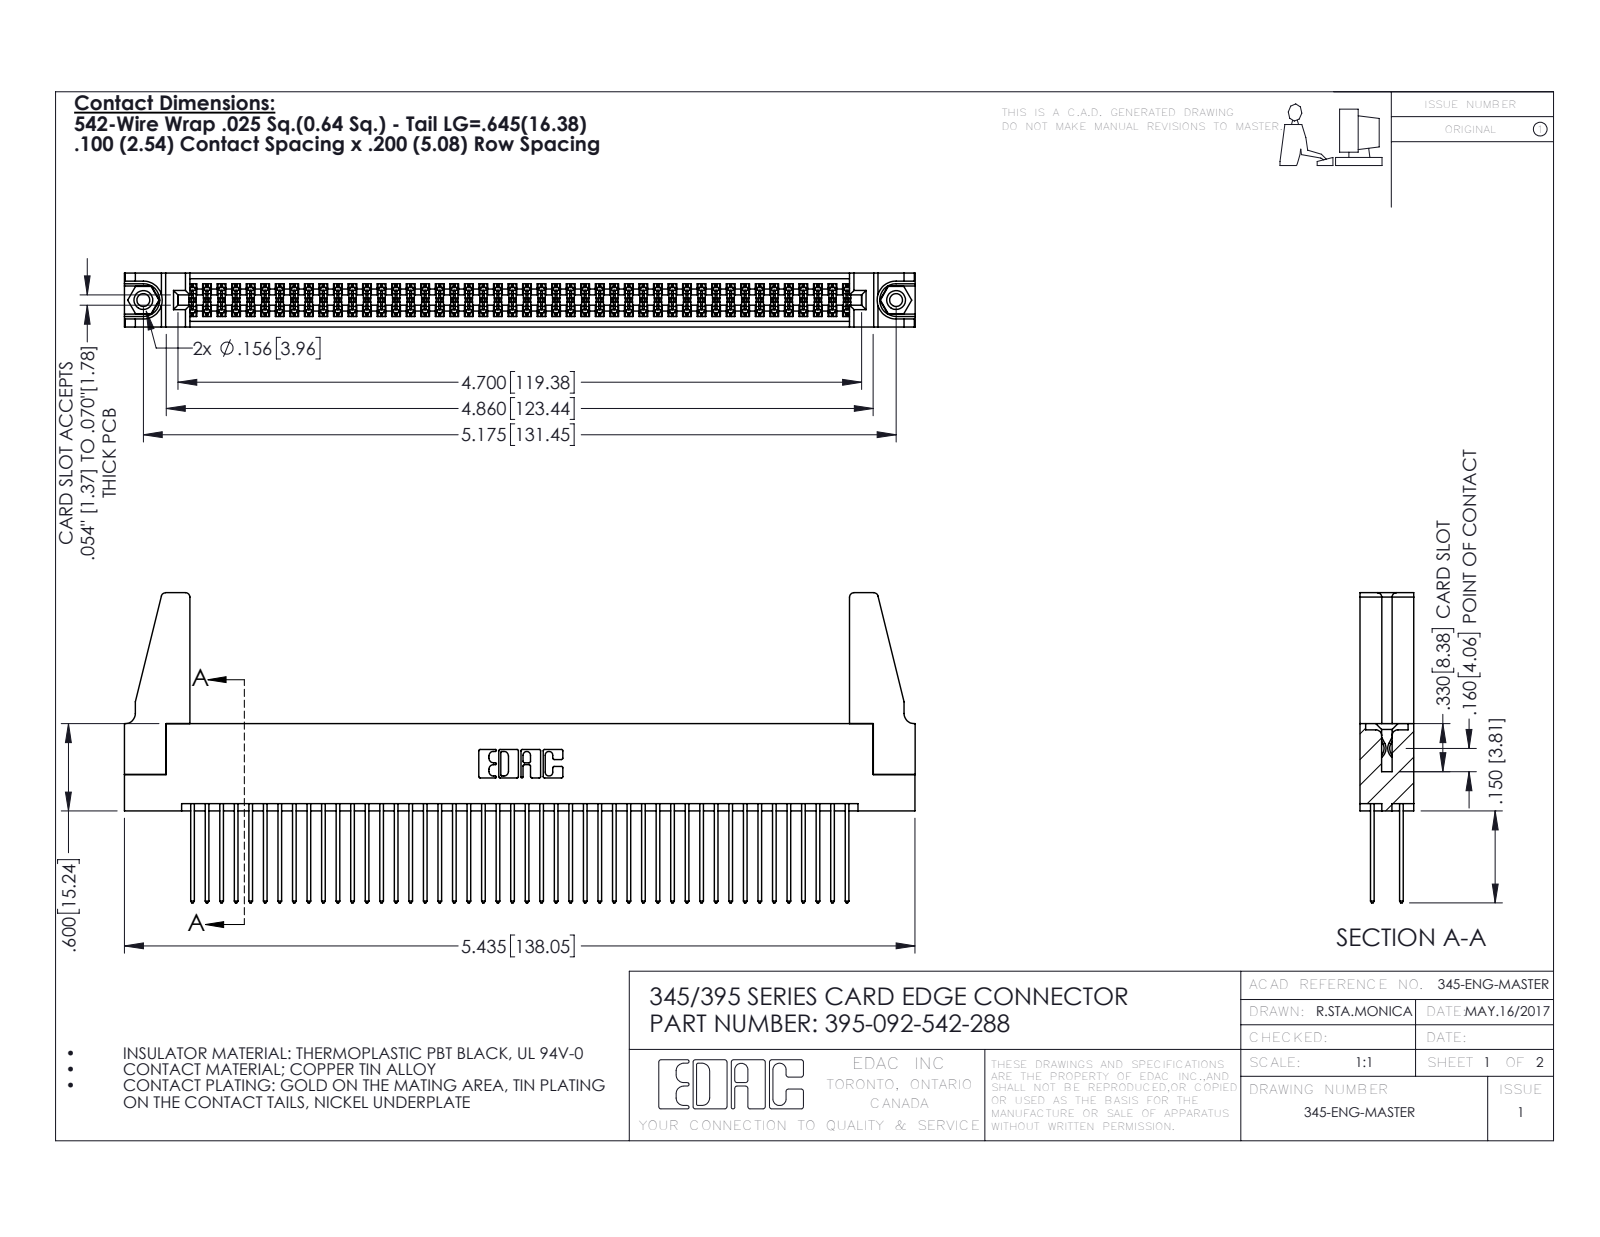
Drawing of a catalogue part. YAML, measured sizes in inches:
part_name: "395-092-542-288; 345-220-078_345-220-088; 345-292-001_345-293-142; 345 Part_Flush Mounting Lugs - 0.156 Dia-TH (+1 more)"
step_written_by: "SolidWorks 2016 (CONFIG_CONTROL_DESIGN)"
units: inches
bodies: {solids: 97, faces: 4850, planar: 3188, cylindrical: 1646, other: 16}
overall_size: [5.436, 2.132, 0.37]
volume: 1.045
surface_area: 39.86
round_holes:
  - {diameter: 0.089, count: 2}
  - {diameter: 0.125, count: 2}
  - {diameter: 0.156, count: 2}
  - {diameter: 0.064, count: 1}
round_bosses_or_shafts:
  - {diameter: 0.155, count: 2}
partial_cylinders:
  - {radius: 0.006, count: 138}
  - {radius: 0.01, count: 92}
  - {radius: 0.01, count: 22}
  - {radius: 0.03, count: 8}
  - {radius: 0.007, count: 6}
  - {radius: 0.031, count: 6}
  - {radius: 0.026, count: 3}
  - {radius: 0.014, count: 2}
face_to_face_distances: [0.072, 0.298, 0.2, 0.098, 0.272, 0.025, 0.37, 0.225, 0.175, 0.149]
hole_center_spacings: [0.27, 4.939, 5.175]
